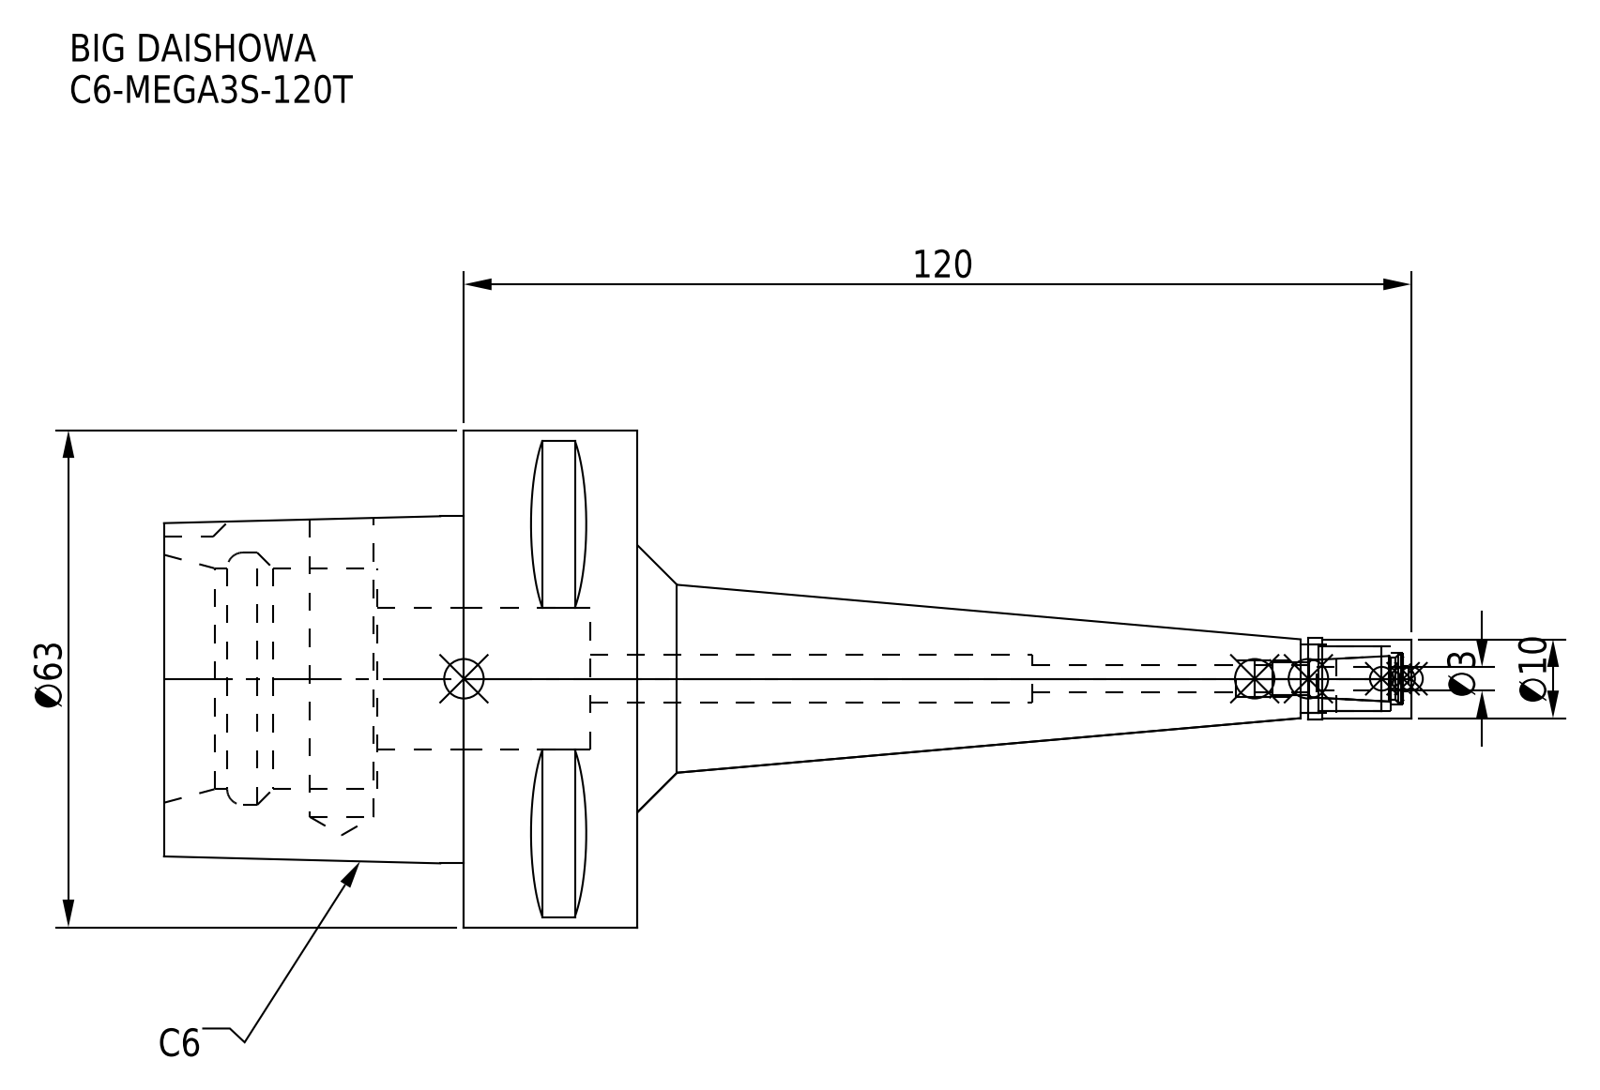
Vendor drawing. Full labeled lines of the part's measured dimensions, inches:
Part name (STEP PRODUCT): C6-MEGA3S-120T_1.stp; MGN3S_1.stp; C6-MEGA3S-120T; C6-MEGA3S-120T-030-FreeParts (+3 more)
STEP written by: SolidWorks 2019 (CONFIG_CONTROL_DESIGN)
Units: inches
Bodies: 2 solids, 93 faces (38 planar, 37 cylindrical, 18 other)
Overall size (bounding box): 6.22 × 2.48 × 2.48
Volume: 7.164 in³ · Surface area: 41.71 in²
Round holes (diameter × count): ⌀0.13 ×1, ⌀0.134 ×1, ⌀0.185 ×1, ⌀0.236 ×1, ⌀0.26 ×1, ⌀0.319 ×1, ⌀0.323 ×1, ⌀0.343 ×1, ⌀0.709 ×1, ⌀1.102 ×1, ⌀1.26 ×1
Round bosses / shafts (diameter × count): ⌀2.48 ×1, ⌀0.406 ×1, ⌀0.394 ×1
Partial cylindrical surfaces — rounded edges, fillets, slot ends (radius × count): R0.197 ×1
Main face-to-face distances: 0.866, 1.063, 2.362, 1.496, 0.433, 1.299, 0.98, 2.181, 0.236, 0.63
